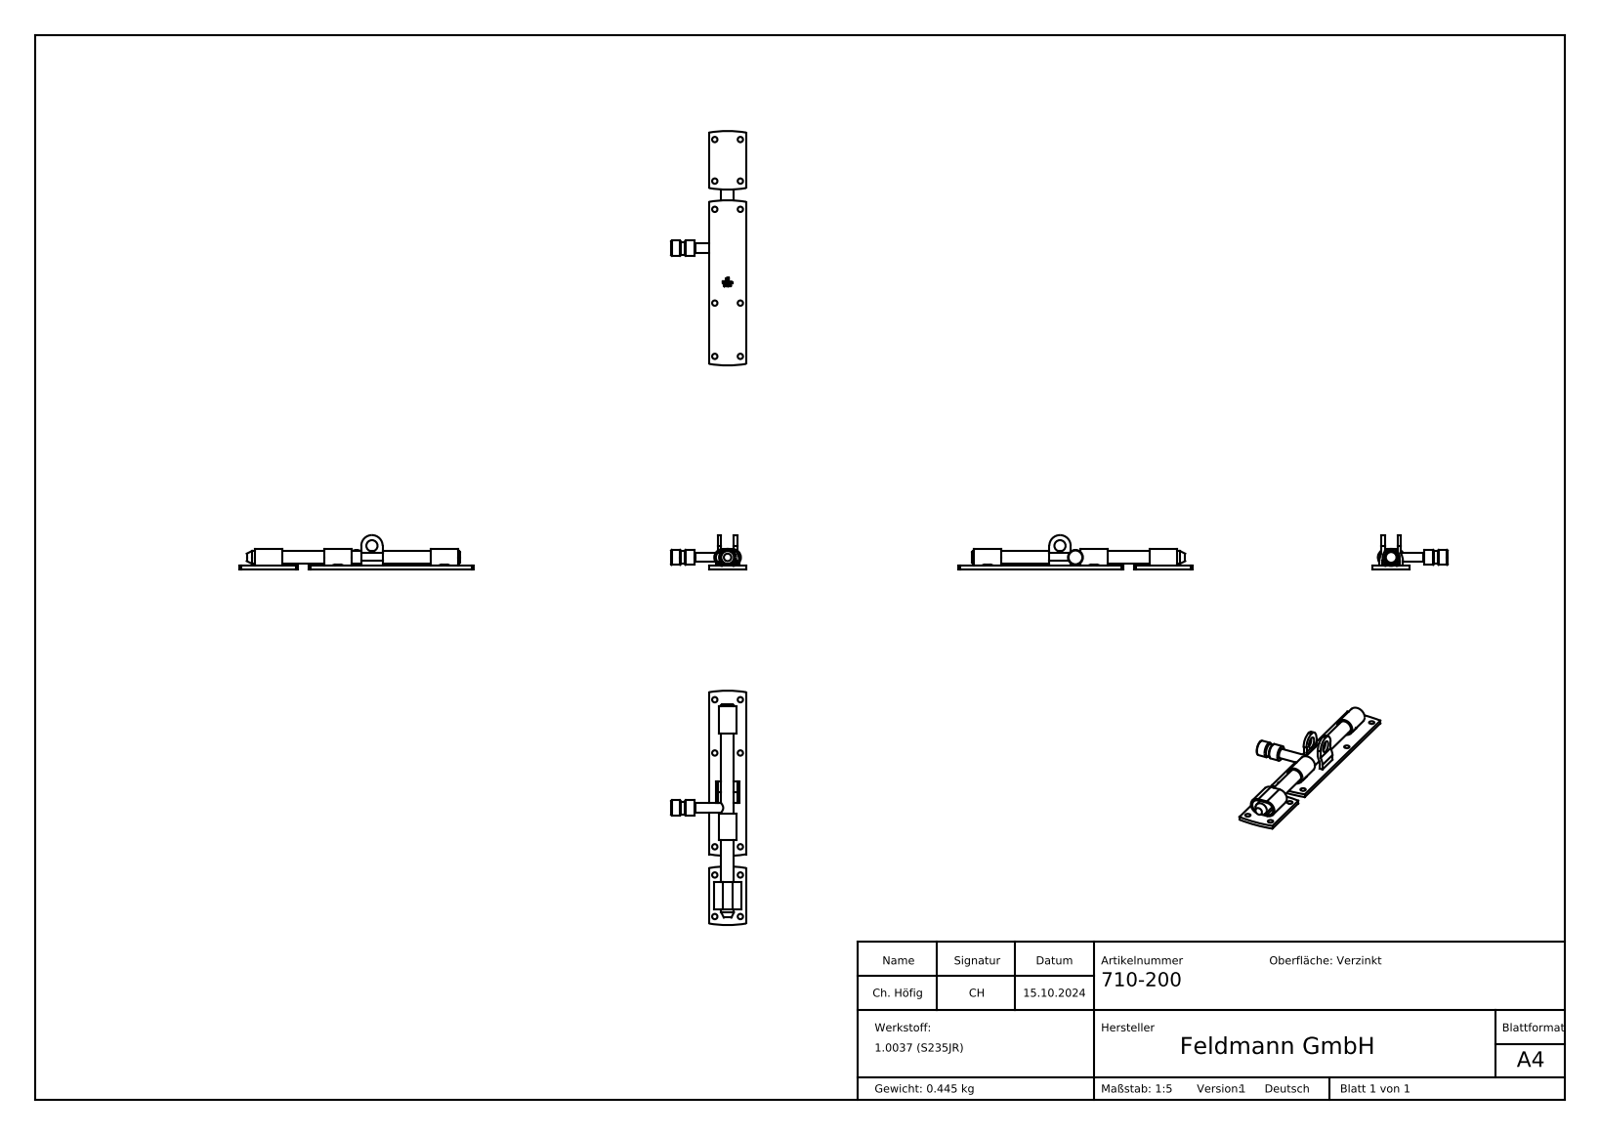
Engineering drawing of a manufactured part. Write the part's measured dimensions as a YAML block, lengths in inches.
part_name: "710-200; 710-XX0 Teil3_710-200 Teil3; 710-XX0 Teil1_710-200 Teil1; 710-XX0 Teil2_710-200 Teil2"
step_written_by: "SolidWorks 2018 (CONFIG_CONTROL_DESIGN)"
units: inches
bodies: {solids: 3, faces: 315, planar: 161, cylindrical: 47, other: 107}
overall_size: [8.661, 2.776, 1.26]
volume: 3.479
surface_area: 55.19
round_holes:
  - {diameter: 0.197, count: 10}
  - {diameter: 0.413, count: 1}
  - {diameter: 0.512, count: 1}
round_bosses_or_shafts:
  - {diameter: 0.472, count: 2}
  - {diameter: 0.63, count: 1}
  - {diameter: 0.551, count: 1}
  - {diameter: 0.346, count: 1}
partial_cylinders:
  - {radius: 0.079, count: 8}
  - {radius: 4.048, count: 4}
  - {radius: 0.394, count: 3}
  - {radius: 0.256, count: 2}
  - {radius: 0.315, count: 2}
  - {radius: 0.404, count: 2}
  - {radius: 0.522, count: 2}
face_to_face_distances: [0.118, 1.378, 0.079, 0.059, 0.571, 0.748, 0.335, 1.043, 0.669, 0.787]
hole_center_spacings: [0.945, 1.043, 1.407, 1.535, 1.803, 1.969, 2.183, 2.579]
